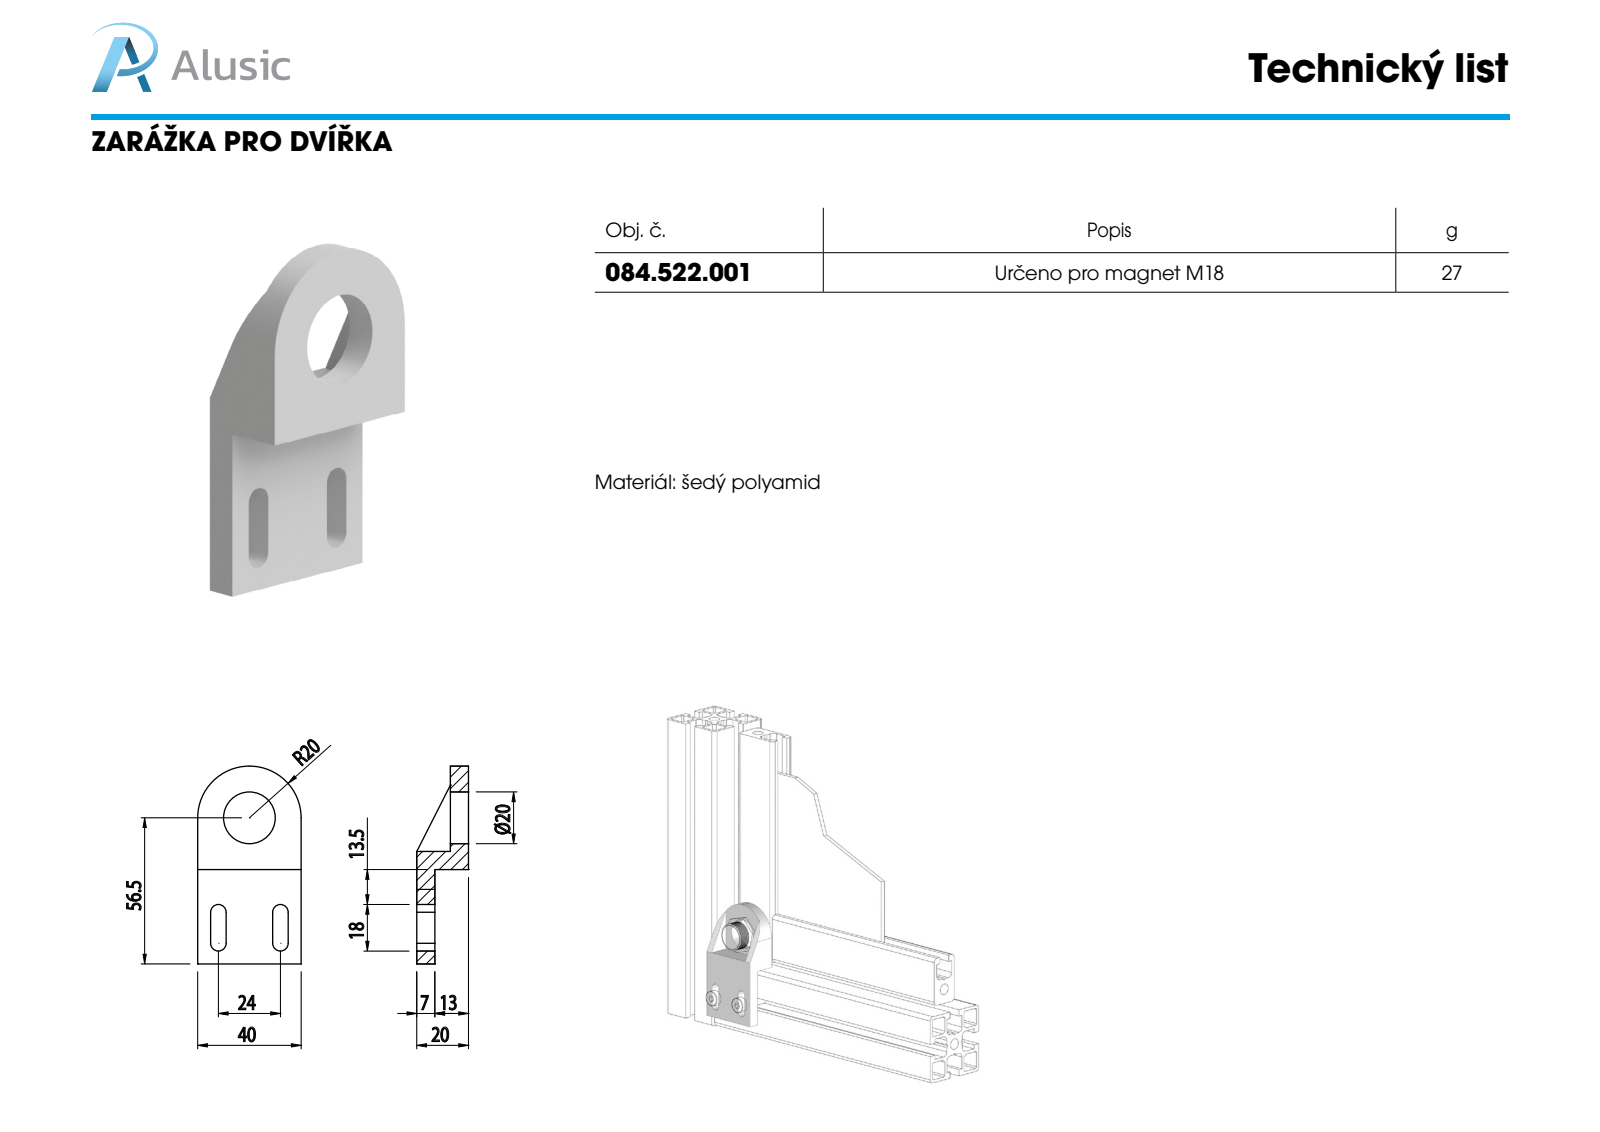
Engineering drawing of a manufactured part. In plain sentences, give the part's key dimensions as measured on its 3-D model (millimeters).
The part is named "084.522.001". Its 3-D file was written by "SolidWorks 2011 (CONFIG_CONTROL_DESIGN)". It is 1 solid with 25 faces: 17 planar, 8 cylindrical and 0 other. Overall it measures 76.5 by 40 by 20 millimeters. Its volume is 21 699 cubic millimeters and its surface area 9 096 square millimeters. Round holes: 1 of diameter 20. Partial cylindrical surfaces (rounded edges, fillets, slot ends): 4 of radius 3, 1 of radius 20. The main face-to-face distances are 7, 13, 20, 6, 40, 4.5, 35.5, 36.5, 43.5, 5.
